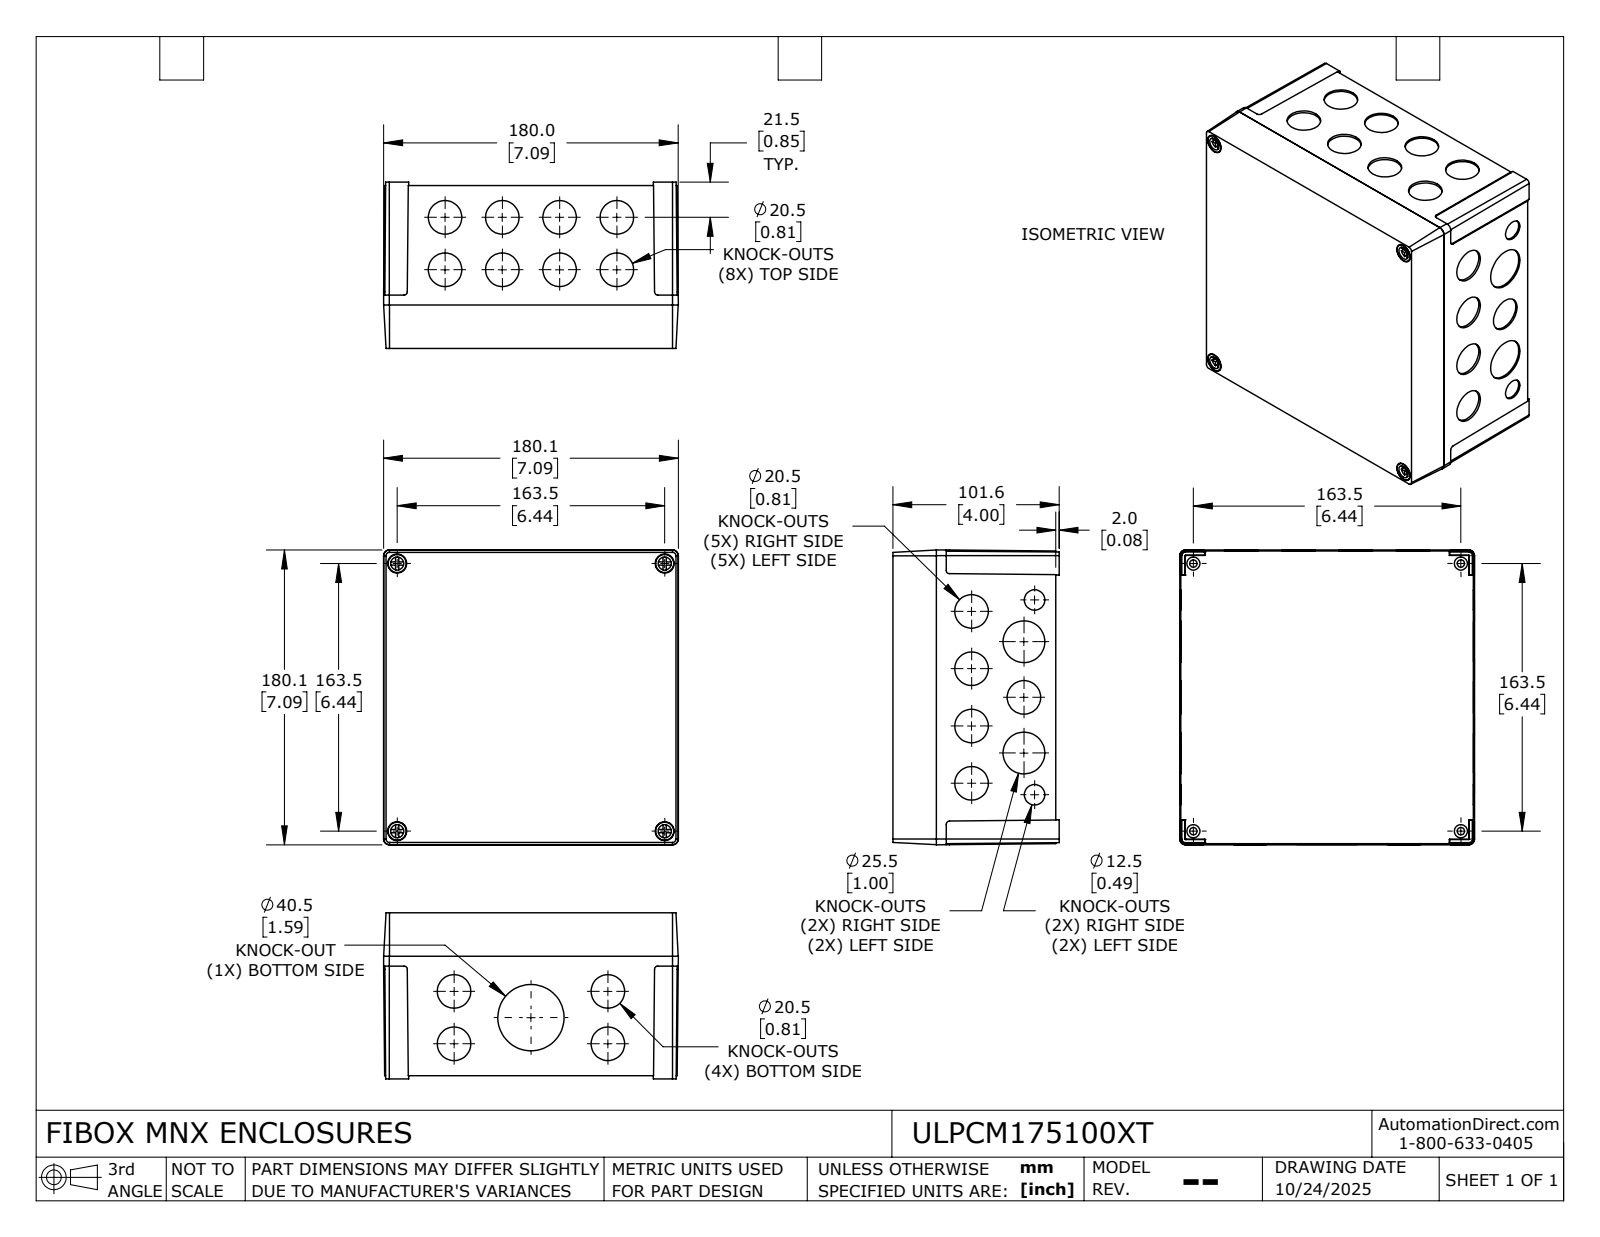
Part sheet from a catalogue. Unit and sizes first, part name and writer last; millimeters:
Units: millimetres
Overall size (bounding box): 180.1 × 180.1 × 101.6
Round holes (diameter × count): ⌀3.2 ×12, ⌀4 ×12, ⌀20.5 ×9, ⌀4.5 ×4, ⌀8 ×4, ⌀11.6 ×4, ⌀12.5 ×2, ⌀25.5 ×2, ⌀40.5 ×1
Round bosses / shafts (diameter × count): ⌀8 ×12, ⌀2.5 ×8, ⌀11 ×4, ⌀7.2 ×4
Partial cylindrical surfaces — rounded edges, fillets, slot ends (radius × count): R2 ×4, R5 ×4
Main face-to-face distances: 4.2, 99.6, 2.5, 97.1, 3, 96.6, 94.1, 0.65, 3.55, 24.1
Hole centre spacings: 33.85, 50, 72.8, 82.59, 121.66, 132.27, 138.92, 148.66
Volume: 461 394 mm³ · Surface area: 285 236 mm²
Bodies: 12 solids, 478 faces (314 planar, 124 cylindrical, 40 other)
Part name (STEP PRODUCT): ULPCM175100XT_Default
STEP written by: SolidWorks 2024 (CONFIG_CONTROL_DESIGN)
